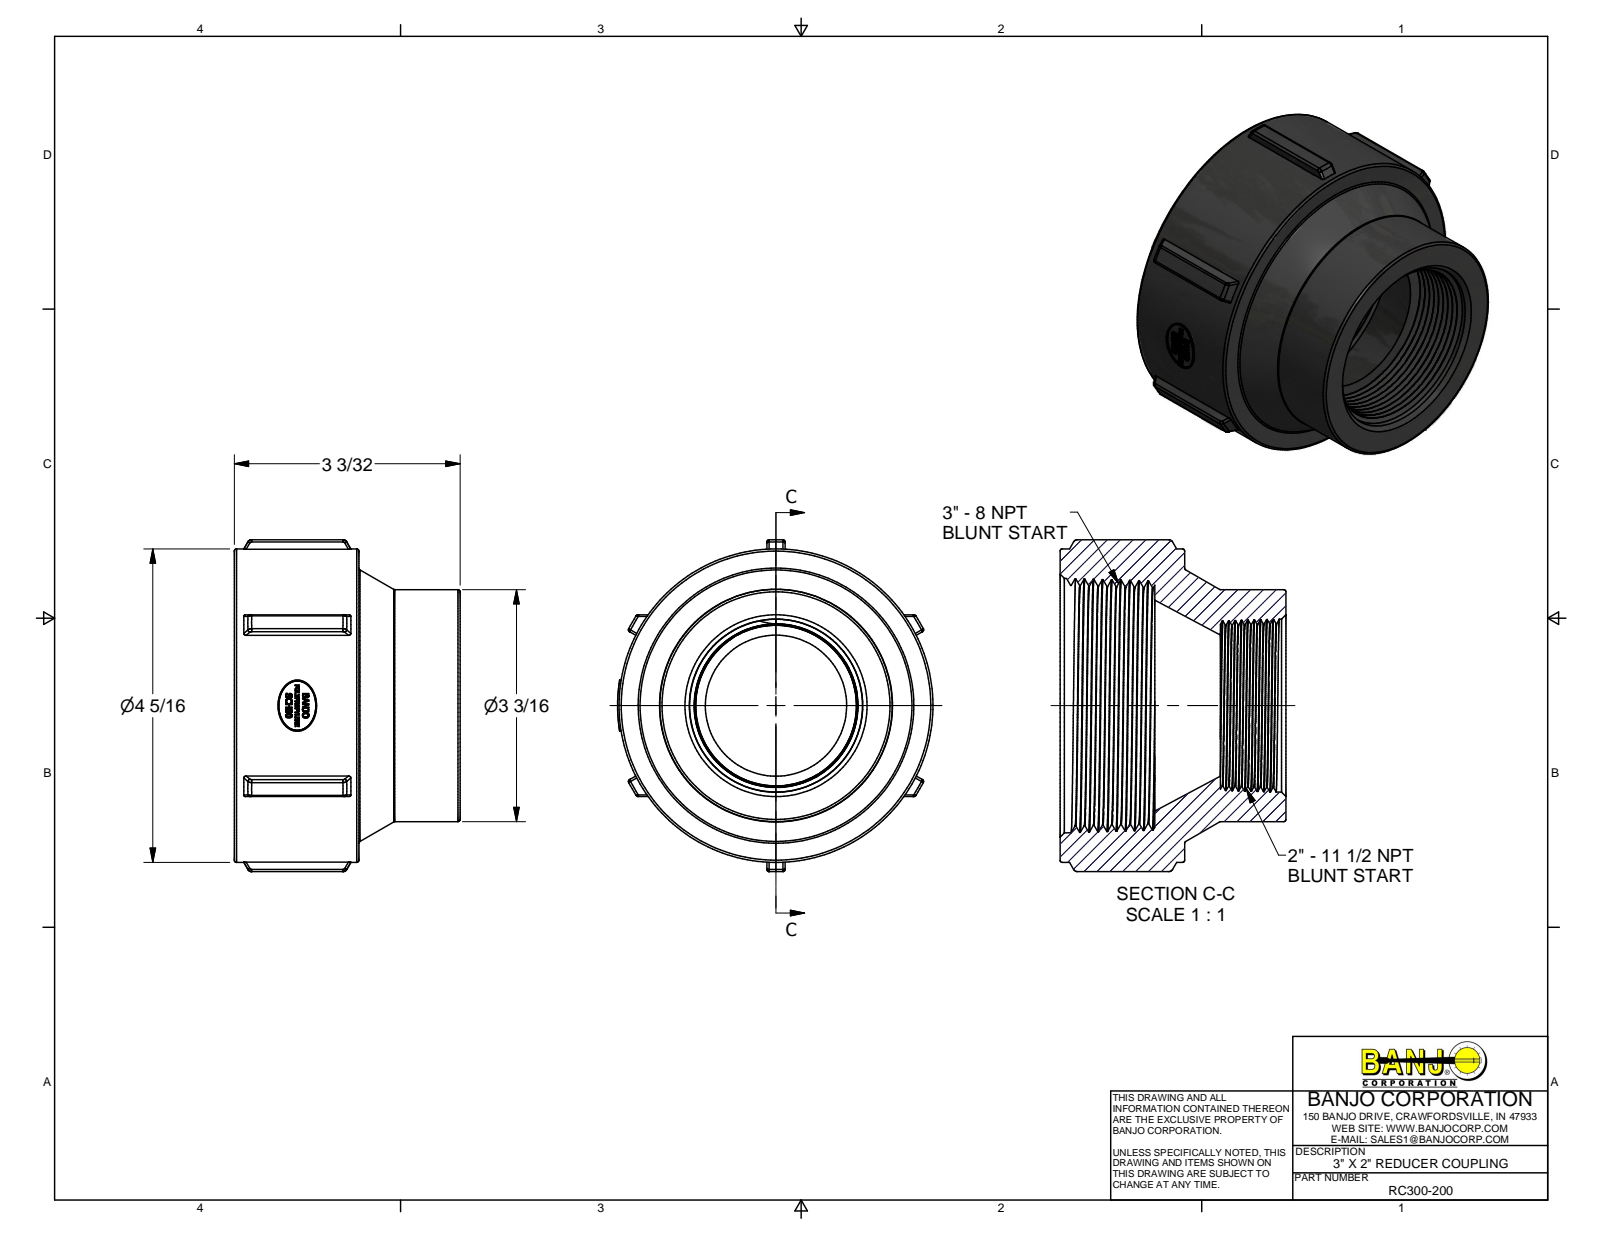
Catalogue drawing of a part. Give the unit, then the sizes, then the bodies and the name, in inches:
Units: inches
Overall size (bounding box): 4.563 × 4.33 × 3.1
Round bosses / shafts (diameter × count): ⌀4.31 ×1, ⌀3.19 ×1
Partial cylindrical surfaces — rounded edges, fillets, slot ends (radius × count): R0.03 ×12, R0.658 ×1, R0.971 ×1, R2.175 ×1
Main face-to-face distances: 1.71, 3.1, 1.39, 0.9, 1.3, 0.41, 1.8, 2.2, 0.49, 4.563
Volume: 17.41 in³ · Surface area: 97.87 in²
Bodies: 1 solid, 504 faces (162 planar, 54 cylindrical, 288 other)
Part name (STEP PRODUCT): RC300-200
STEP written by: Autodesk Inventor 2014 (AUTOMOTIVE_DESIGN)
